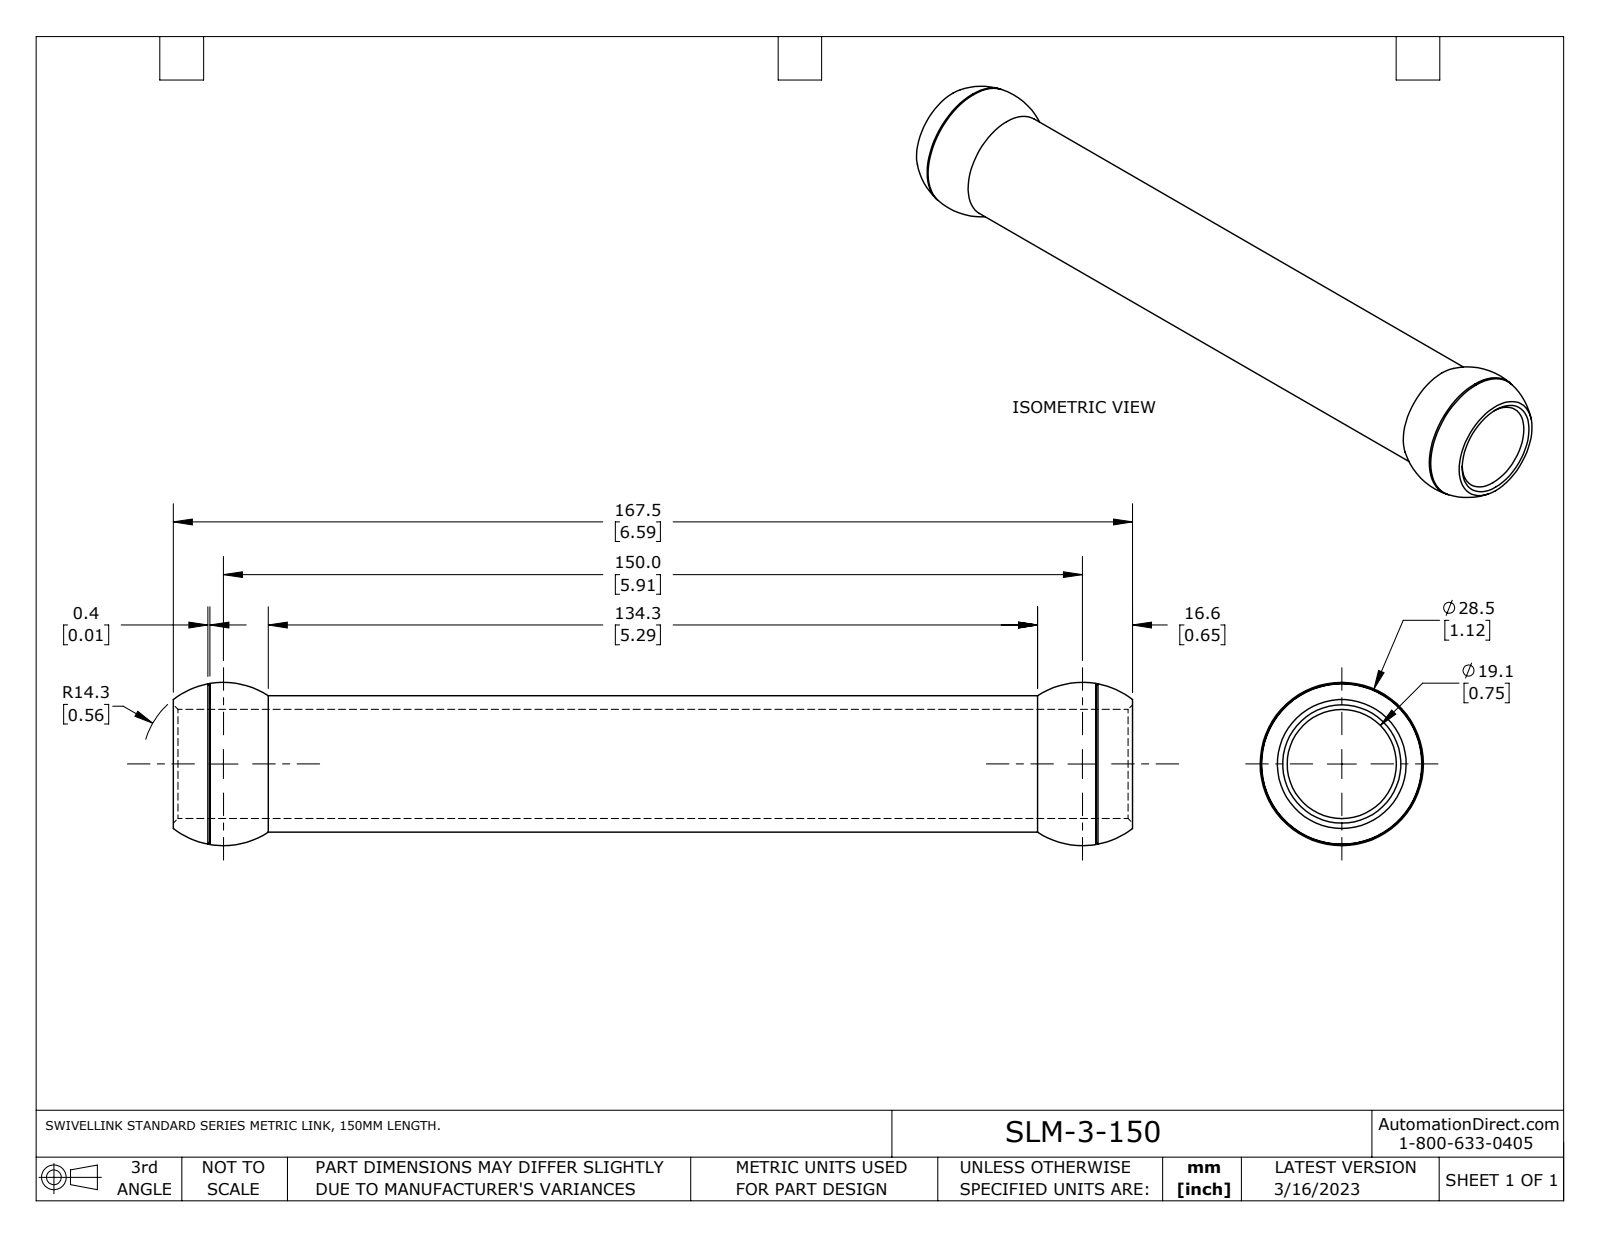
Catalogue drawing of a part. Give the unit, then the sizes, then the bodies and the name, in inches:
Units: inches
Overall size (bounding box): 6.594 × 1.122 × 1.122
Round holes (diameter × count): ⌀0.75 ×1
Round bosses / shafts (diameter × count): ⌀0.937 ×1
Main face-to-face distances: 6.594
Volume: 1.879 in³ · Surface area: 36.04 in²
Bodies: 1 solid, 12 faces (2 planar, 2 cylindrical, 8 other)
Part name (STEP PRODUCT): SLM-3-150
STEP written by: SolidWorks 2021 (AUTOMOTIVE_DESIGN)
